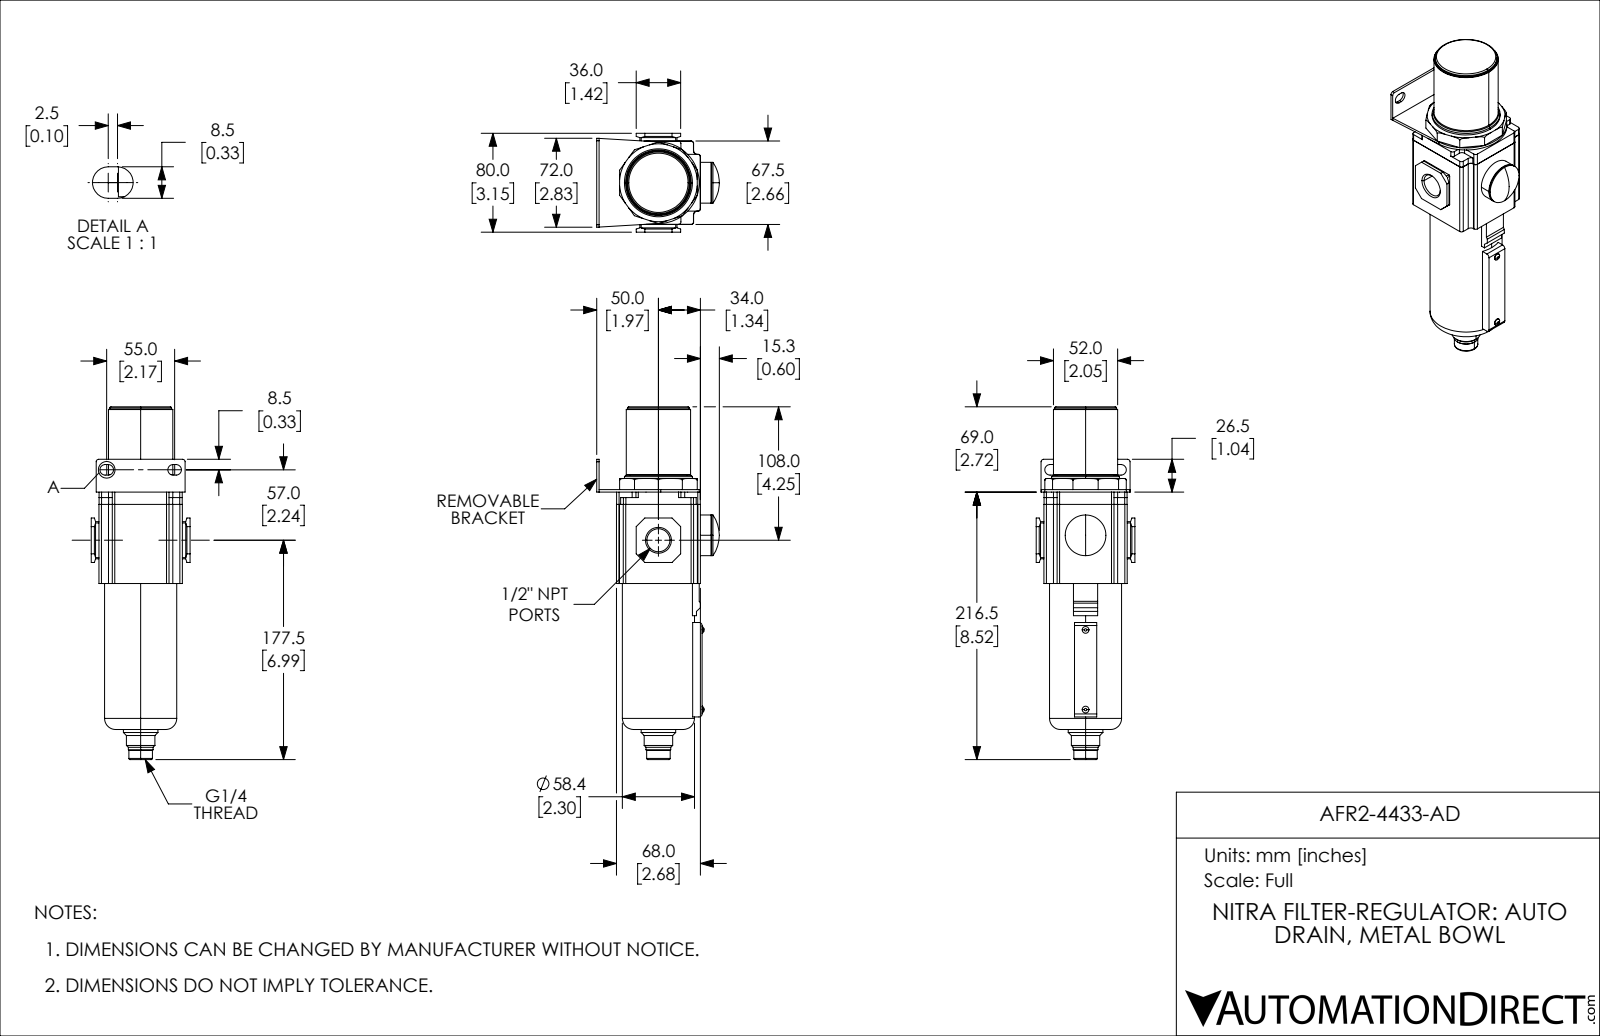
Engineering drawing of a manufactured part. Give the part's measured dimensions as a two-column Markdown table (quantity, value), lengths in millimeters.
| quantity | value |
| --- | --- |
| part name | AFR2-4433-AD |
| STEP written by | SolidWorks 2019 (CONFIG_CONTROL_DESIGN) |
| units | millimeters |
| bodies | 1 solid, 237 faces (124 planar, 73 cylindrical, 40 other) |
| overall size | 285.5 × 99.28 × 80 |
| volume | 831 056 mm³ |
| surface area | 77 361 mm² |
| round holes (diameter × count) | 11.45 × 1, 18.63 × 1 |
| round bosses / shafts (diameter × count) | 5.5 × 2, 58.4 × 1, 55 × 1, 52 × 1, 50 × 1, 45.9 × 1, 33 × 1, 28 × 1 |
| partial cylindrical surfaces (radius × count) | 2 × 22, 3 × 12, 4.25 × 4, 2.5 × 2, 33 × 1 |
| main face-to-face distances | 2, 67.5, 67, 68, 16, 14, 69, 84, 76, 6.25 |
